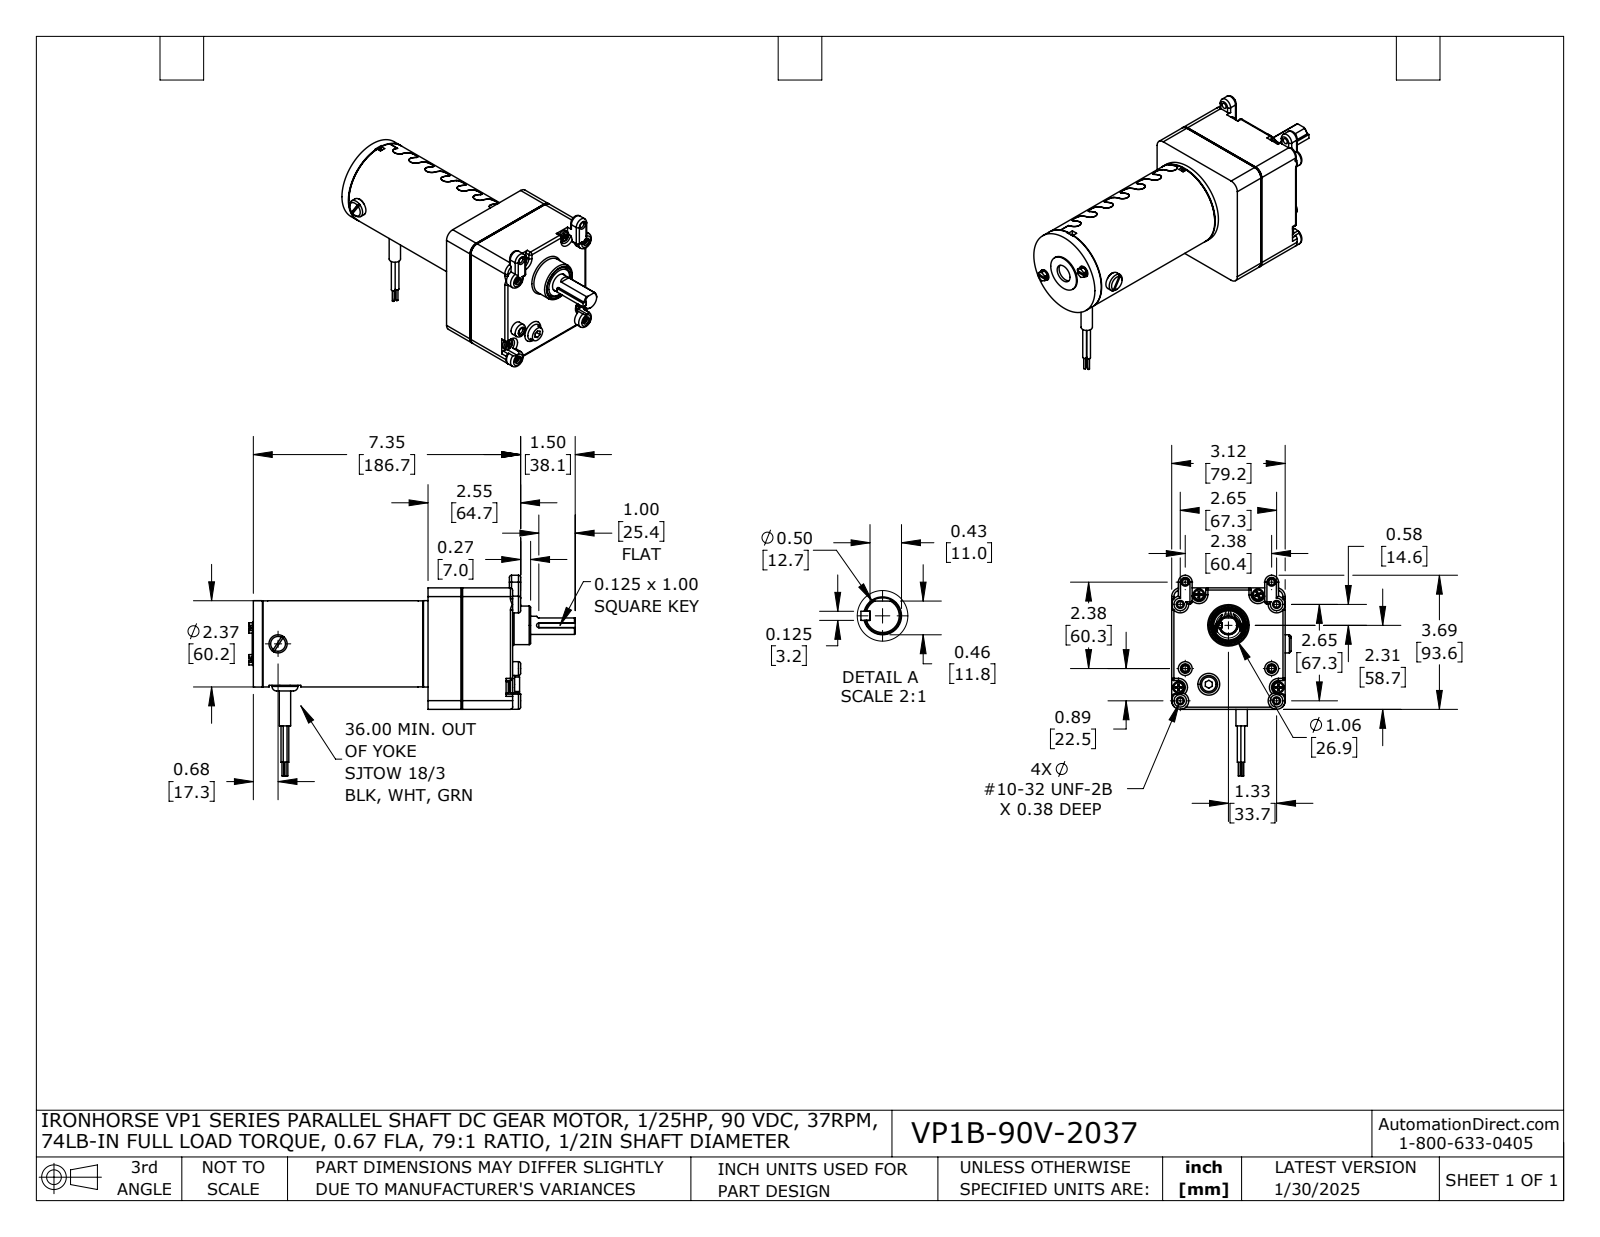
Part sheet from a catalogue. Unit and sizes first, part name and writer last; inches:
Units: inches
Overall size (bounding box): 8.974 × 5.516 × 3.283
Round holes (diameter × count): ⌀0.2 ×11, ⌀0.158 ×8, ⌀0.18 ×4, ⌀0.187 ×2, ⌀0.189 ×2, ⌀0.22 ×2, ⌀0.213 ×1, ⌀0.336 ×1, ⌀0.468 ×1, ⌀0.5 ×1, ⌀0.521 ×1, ⌀0.688 ×1
Round bosses / shafts (diameter × count): ⌀0.314 ×4, ⌀0.313 ×4, ⌀0.136 ×4, ⌀0.105 ×3, ⌀0.052 ×3, ⌀0.5 ×2, ⌀0.466 ×2, ⌀0.44 ×2
Partial cylindrical surfaces — rounded edges, fillets, slot ends (radius × count): R0.06 ×34, R0.062 ×21, R0.156 ×14, R0.151 ×7, R0.161 ×7, R0.15 ×6, R0.12 ×4, R0.235 ×4
Main face-to-face distances: 0.09, 3.12, 1.38, 2.326, 0.946, 0.106, 1.274, 2.22, 3.34, 0.315
Hole centre spacings: 1.68, 2.65, 1.074, 2.729, 3.093, 0.077, 0.297, 0.373
Volume: 12.28 in³ · Surface area: 225.5 in²
Bodies: 20 solids, 916 faces (340 planar, 422 cylindrical, 154 other)
Part name (STEP PRODUCT): VP1B-90V-2037
STEP written by: SolidWorks 2021 (AUTOMOTIVE_DESIGN)
